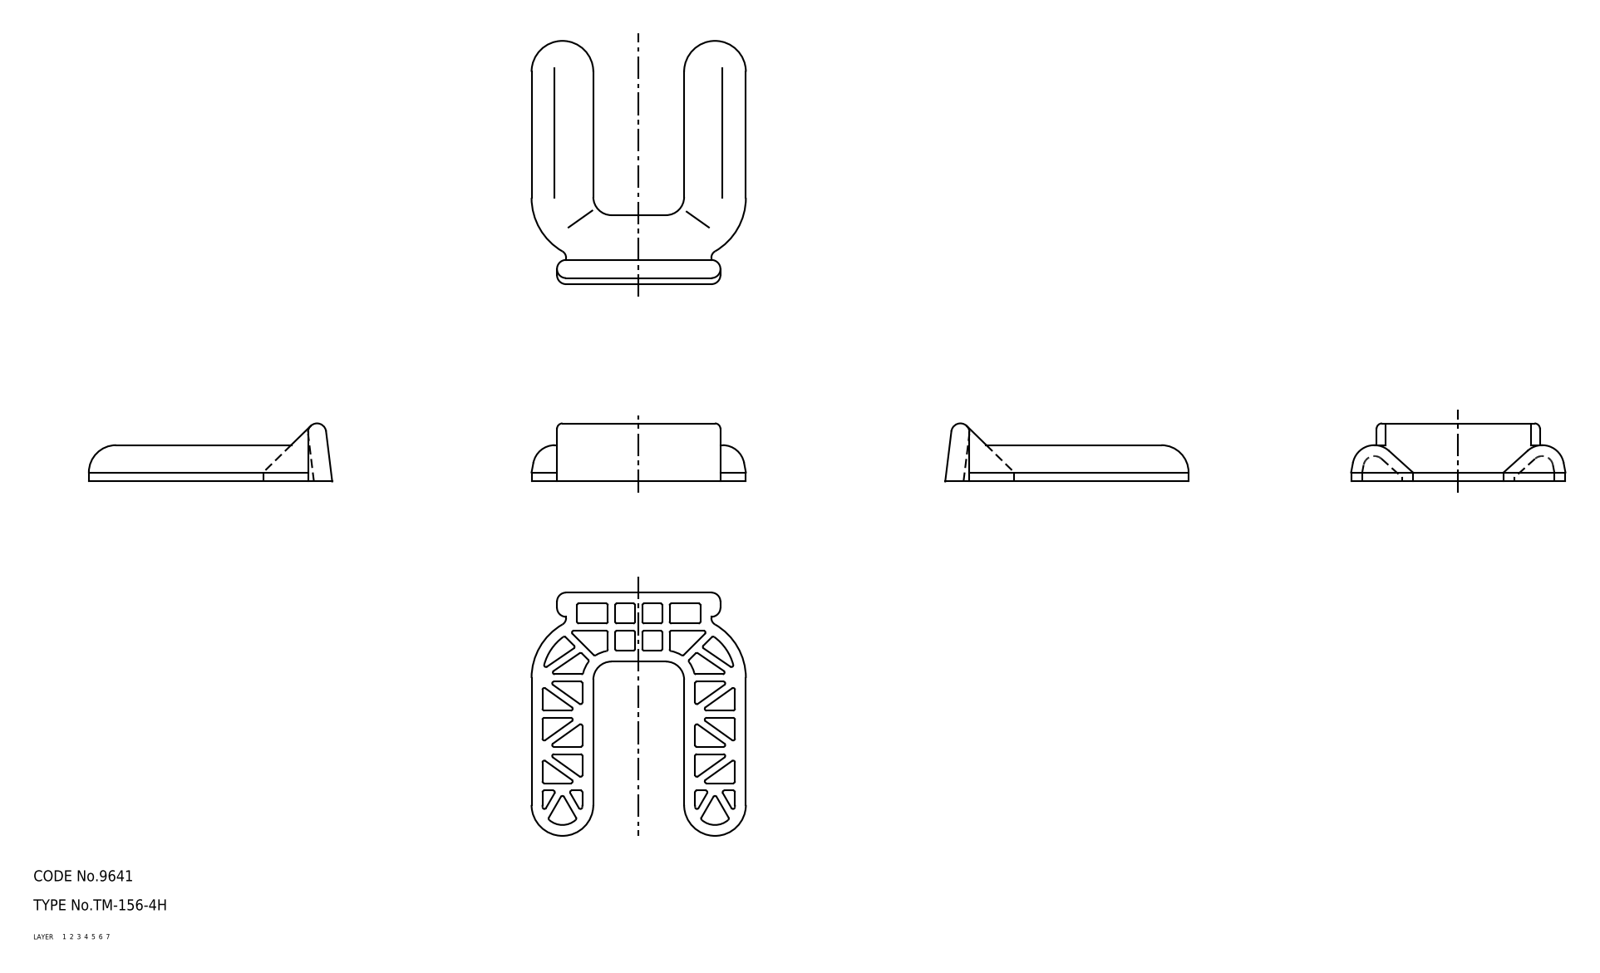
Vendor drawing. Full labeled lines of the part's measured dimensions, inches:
Part name (STEP PRODUCT): holder
STEP written by: CADfix (AUTOMOTIVE_DESIGN)
Units: inches
Bodies: 1 solid, 347 faces (0 planar, 0 cylindrical, 347 other)
Overall size (bounding box): 2.638 × 2.323 × 0.63
Volume: 1 in³ · Surface area: 17.74 in²
